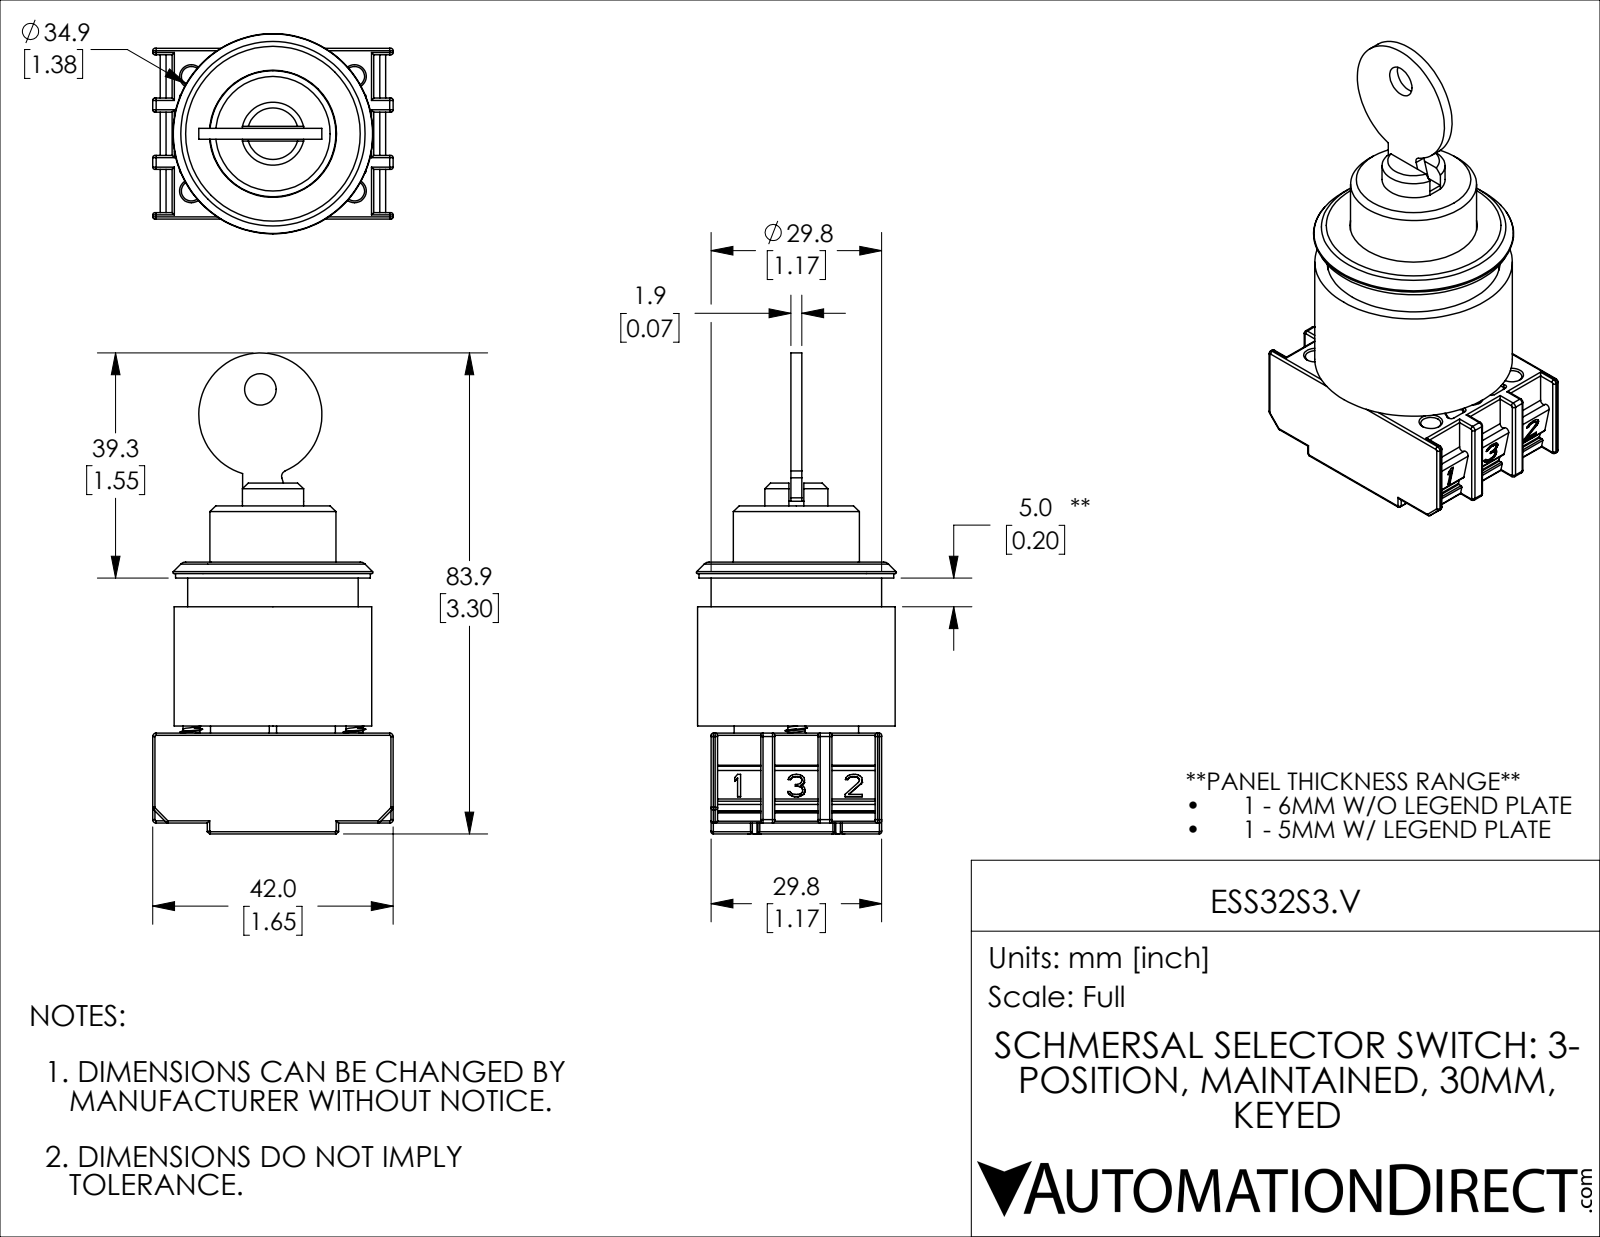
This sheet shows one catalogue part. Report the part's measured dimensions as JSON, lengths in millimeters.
{"part_name": "ESS32S3.V", "step_written_by": "SolidWorks 2019 (CONFIG_CONTROL_DESIGN)", "units": "millimeters", "bodies": {"solids": 6, "faces": 1565, "planar": 586, "cylindrical": 551, "other": 428}, "overall_size": [83.94, 42, 34.93], "volume_mm3": 36829, "surface_area_mm2": 27554, "round_holes": [[3.5, 10], [5.15, 6], [5, 4], [2, 3], [2.5, 2], [2.8, 2], [3, 1], [5.5, 1], [12.1, 1], [12.5, 1], [14, 1], [19, 1]], "round_bosses_or_shafts": [[4.8, 2], [2.93, 2], [34.5, 1], [34, 1], [29.8, 1], [25.5, 1], [22, 1], [21.8, 1]], "partial_cylinders_radius": [[0.4, 120], [0.3, 48], [0.2, 28], [0.6, 8], [0.5, 7], [0.8, 6], [0.1, 2], [0.6, 2]], "face_to_face_distances": [16.1, 13.95, 15.85, 29.8, 1.9, 17.6, 17.35, 18.85, 39.65, 10], "hole_center_spacings": [9.94, 4.24, 4.75, 6, 8.69, 8.99, 10, 10.13]}
